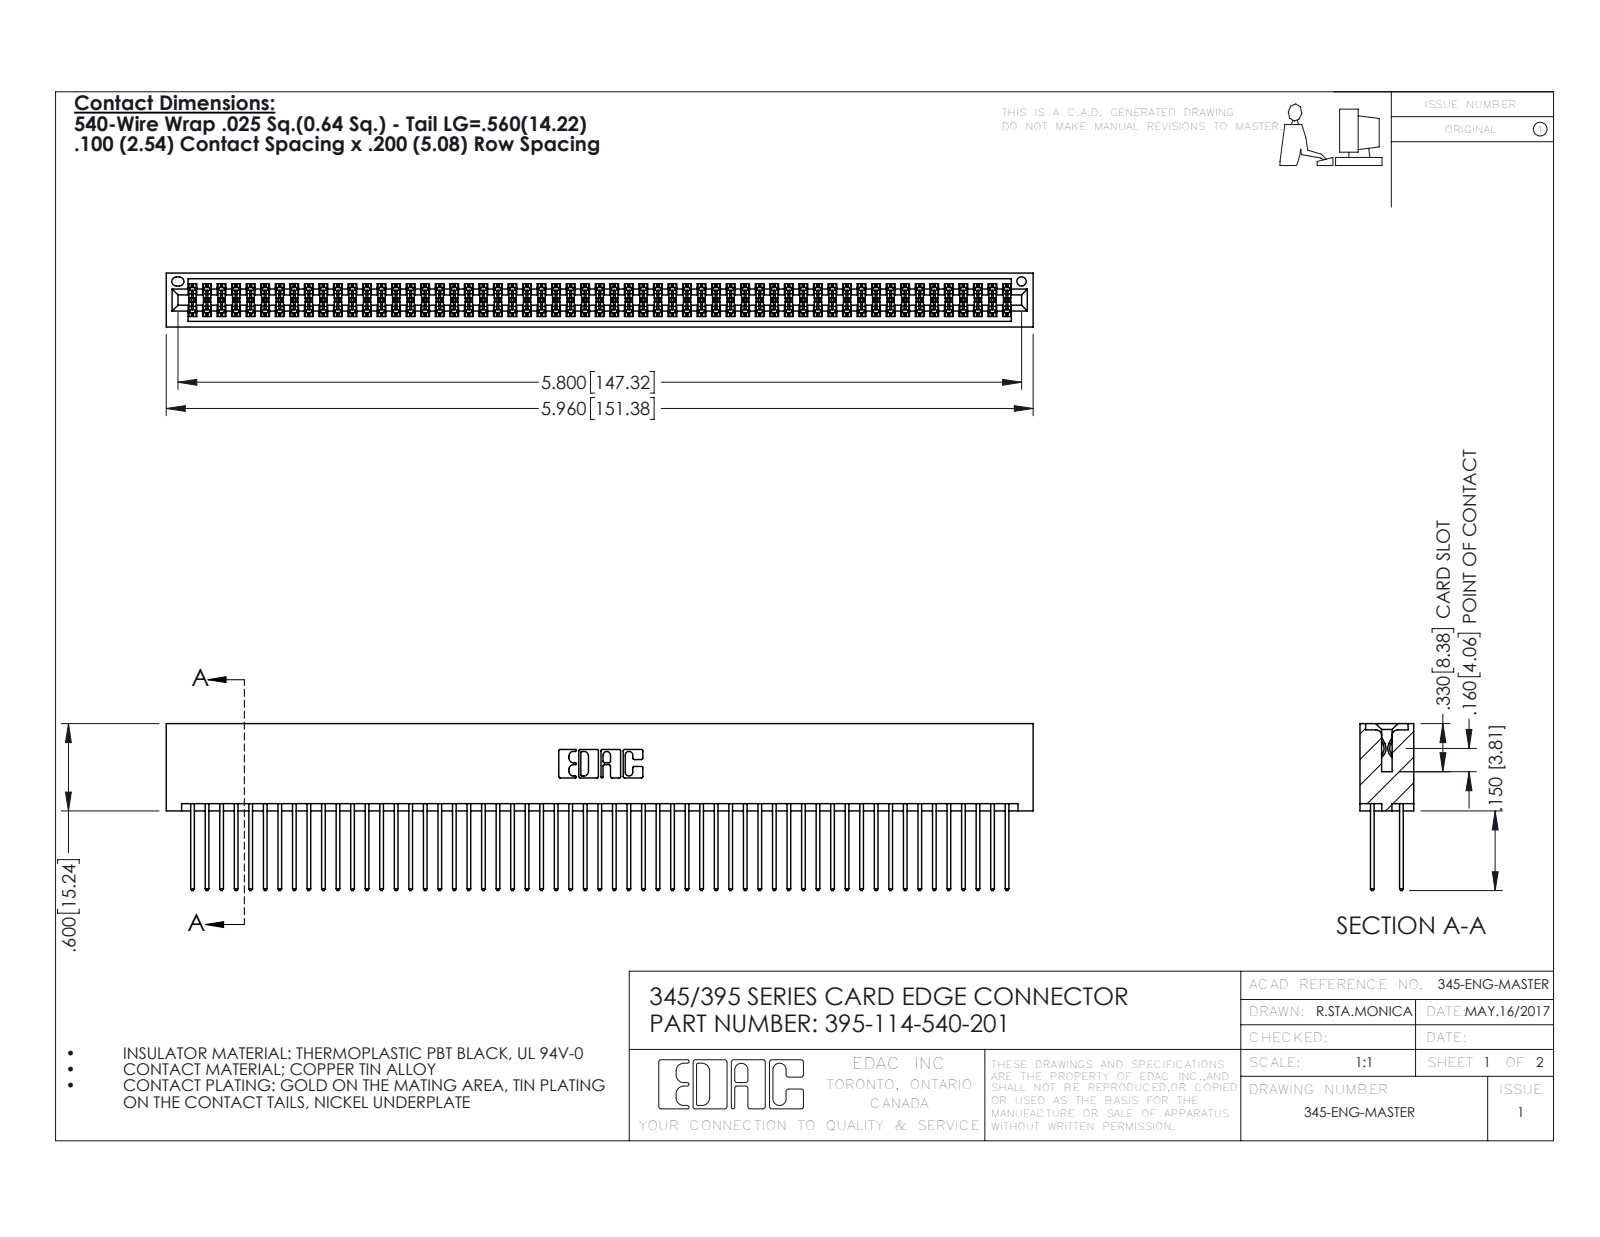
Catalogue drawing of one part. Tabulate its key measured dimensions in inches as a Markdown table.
| quantity | value |
| --- | --- |
| part name | 395-114-540-201; 345-292-001_345-293-140; 345 Part_No Mounting Lugs |
| STEP written by | SolidWorks 2016 (CONFIG_CONTROL_DESIGN) |
| units | inches |
| bodies | 115 solids, 5818 faces (3838 planar, 1980 cylindrical, 0 other) |
| overall size | 5.96 × 1.147 × 0.37 |
| volume | 0.97 in³ |
| surface area | 40.44 in² |
| round holes (diameter × count) | 0.064 × 1 |
| partial cylindrical surfaces (radius × count) | 0.006 × 171, 0.01 × 114, 0.01 × 22, 0.007 × 6, 0.031 × 6, 0.026 × 3, 0.014 × 2, 0.019 × 2 |
| main face-to-face distances | 0.298, 0.072, 0.2, 0.098, 0.272, 0.025, 0.225, 0.37, 0.175, 0.149 |
